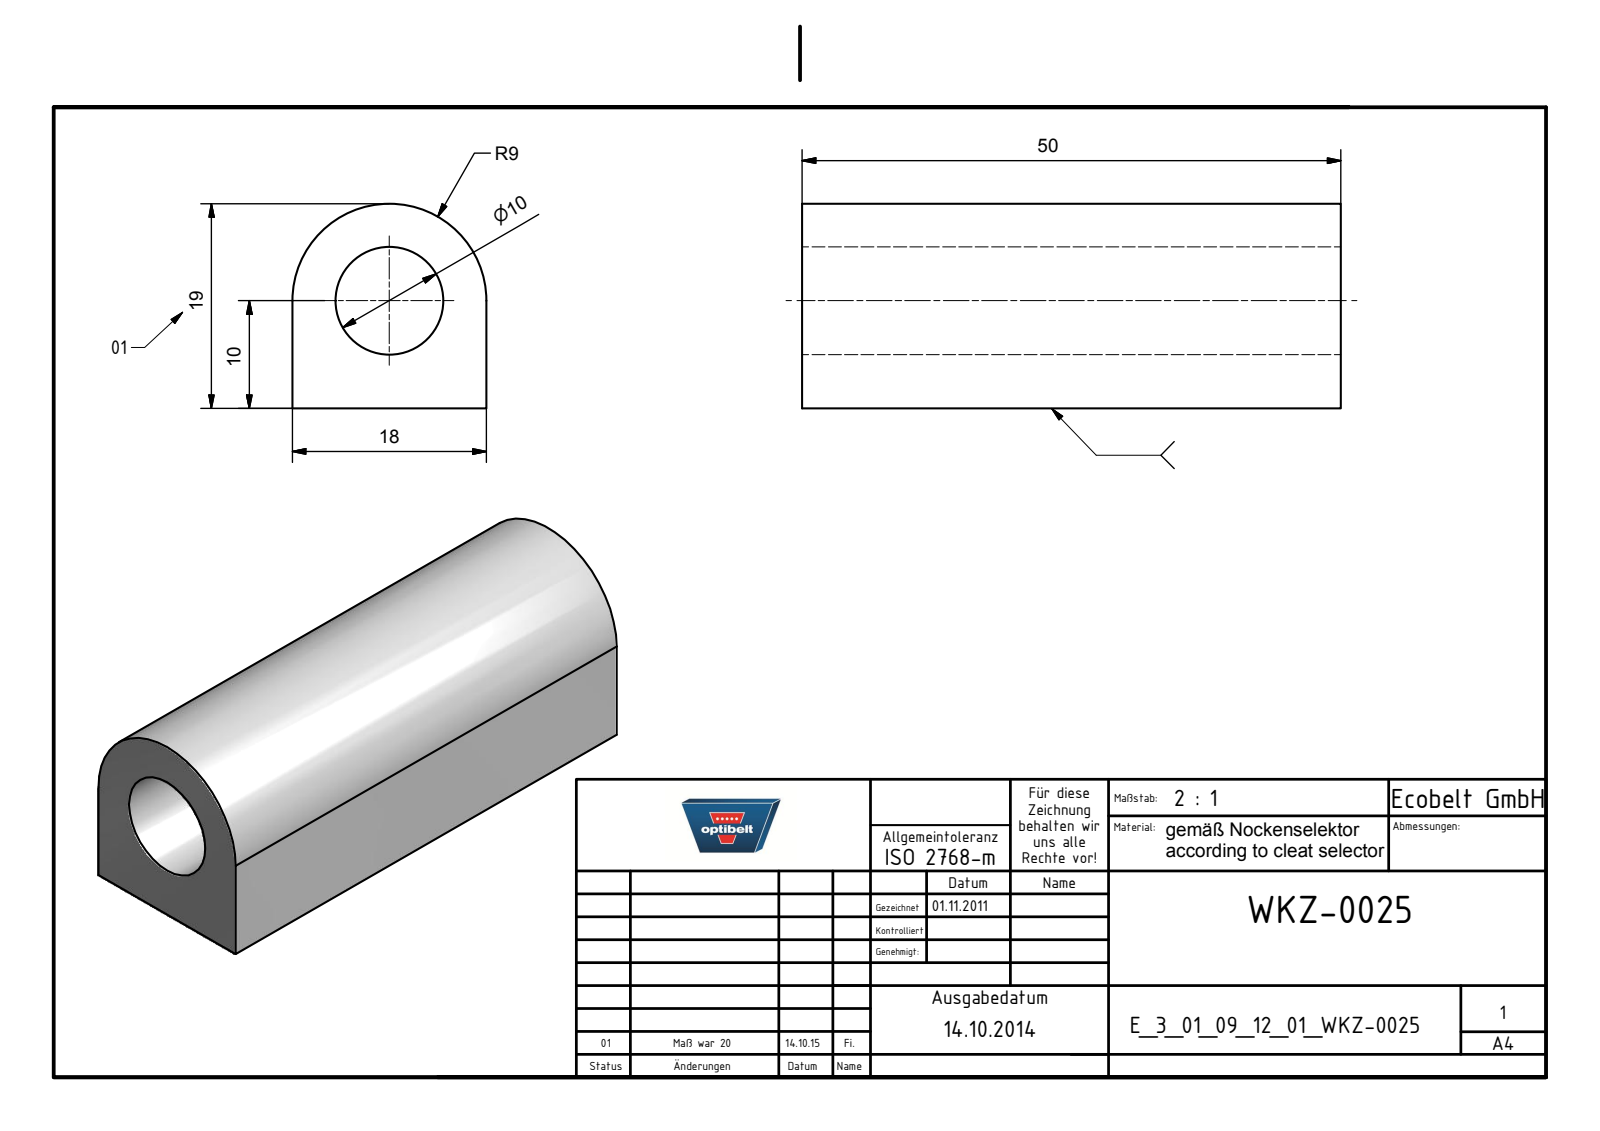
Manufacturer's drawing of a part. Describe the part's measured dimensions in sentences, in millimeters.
The part is named "E_3_01_09_12_01_WKZ-0025". Its 3-D file was written by "Autodesk Inventor 2021 (AUTOMOTIVE_DESIGN)". It is 1 solid with 7 faces: 5 planar, 2 cylindrical and 0 other. Overall it measures 50 by 19 by 18 millimeters. Its volume is 11 435 cubic millimeters and its surface area 5 342 square millimeters. Round holes: 1 of diameter 10. Partial cylindrical surfaces (rounded edges, fillets, slot ends): 1 of radius 9. The main face-to-face distances are 18, 50.
